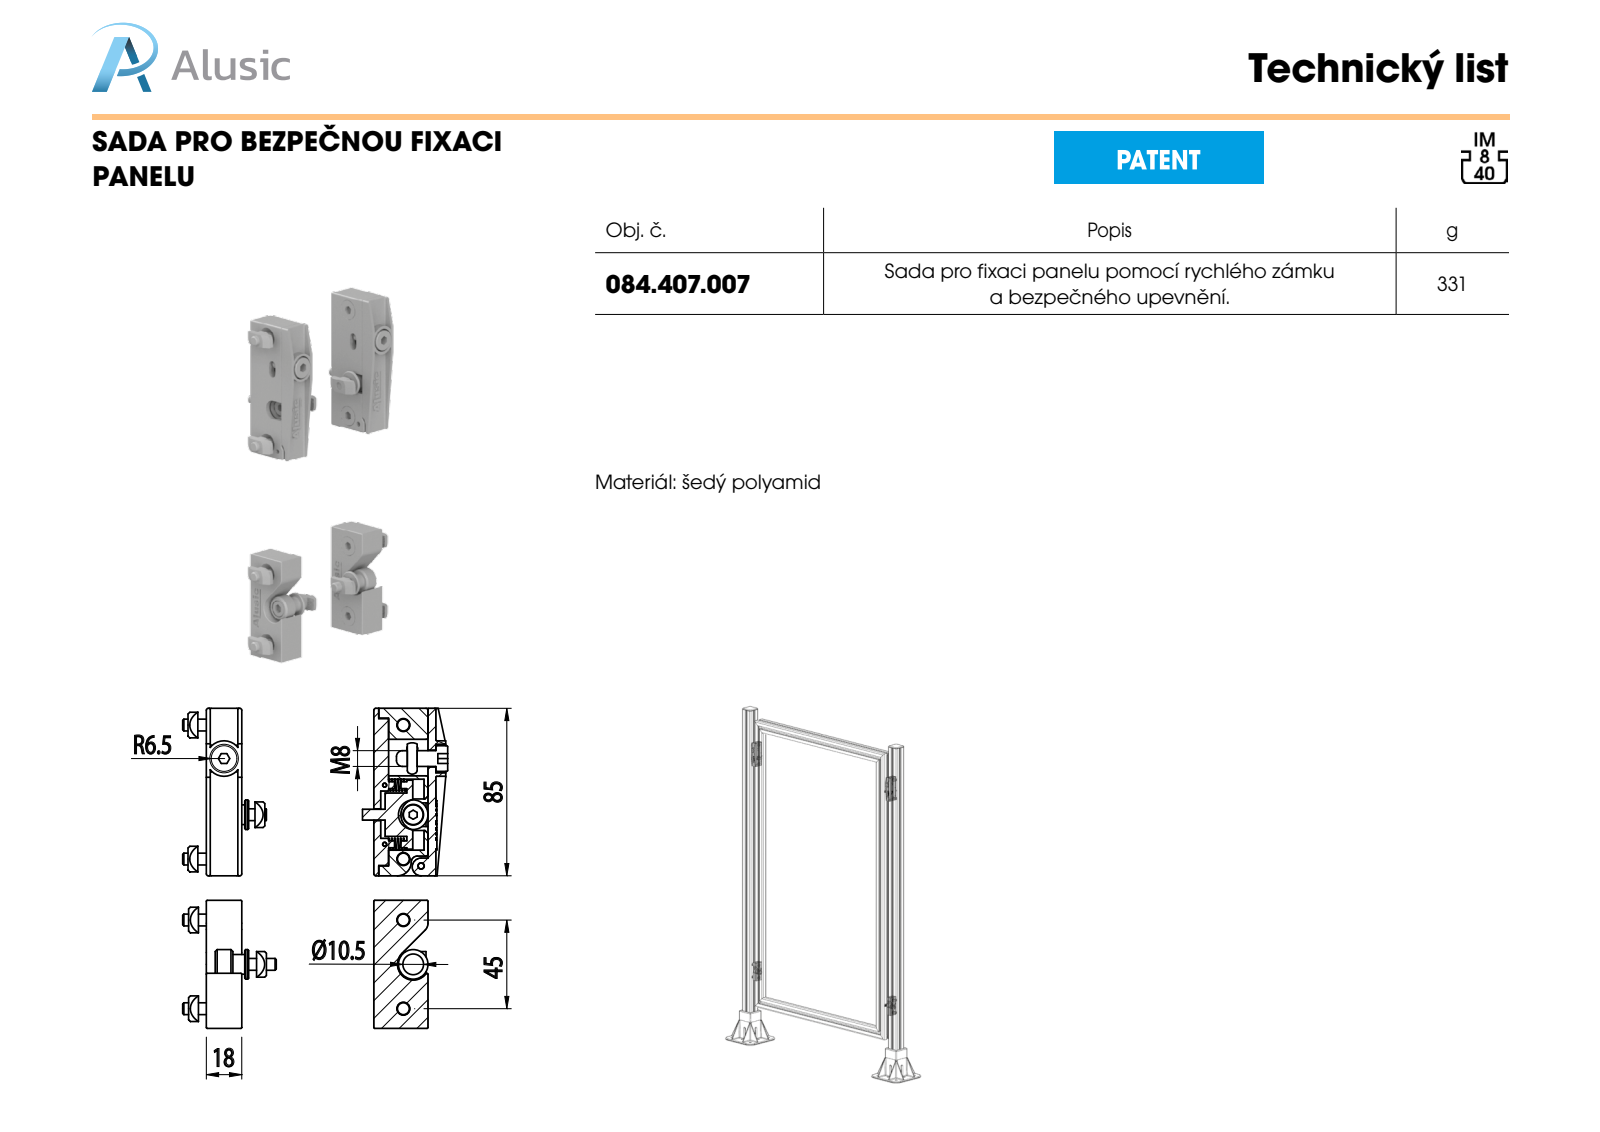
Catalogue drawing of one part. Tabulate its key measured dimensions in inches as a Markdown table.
| quantity | value |
| --- | --- |
| part name | 084.407.103-1; 084.407.103-6; 084.302.114; 084.407.103-3 (+8 more) |
| STEP written by | SolidWorks 2016 (CONFIG_CONTROL_DESIGN) |
| units | inches |
| bodies | 52 solids, 2646 faces (1592 planar, 770 cylindrical, 284 other) |
| overall size | 34.055 × 27.835 × 1.791 |
| volume | 9.839 in³ |
| surface area | 141.3 in² |
| round holes (diameter × count) | 0.197 × 9, 0.26 × 6, 0.079 × 2, 0.236 × 2, 0.335 × 2, 0.413 × 2, 0.571 × 2, 0.118 × 1, 0.126 × 1, 0.217 × 1 |
| round bosses / shafts (diameter × count) | 0.315 × 11, 0.236 × 6, 0.472 × 4, 0.138 × 4, 0.591 × 2, 0.512 × 2, 0.394 × 2, 0.217 × 2 |
| partial cylindrical surfaces (radius × count) | 0.02 × 67, 0.039 × 34, 0.197 × 25, 0.01 × 24, 0.01 × 8, 0.012 × 8, 0.022 × 8, 0.028 × 8 |
| main face-to-face distances | 26.181, 0.709, 0.236, 1.083, 0.098, 0.984, 25.472, 26.89, 0.472, 26.417 |
| hole center spacings | 0.907, 1.122, 0.821, 26.181, 26.205, 29.765, 30.65, 0.067 |
